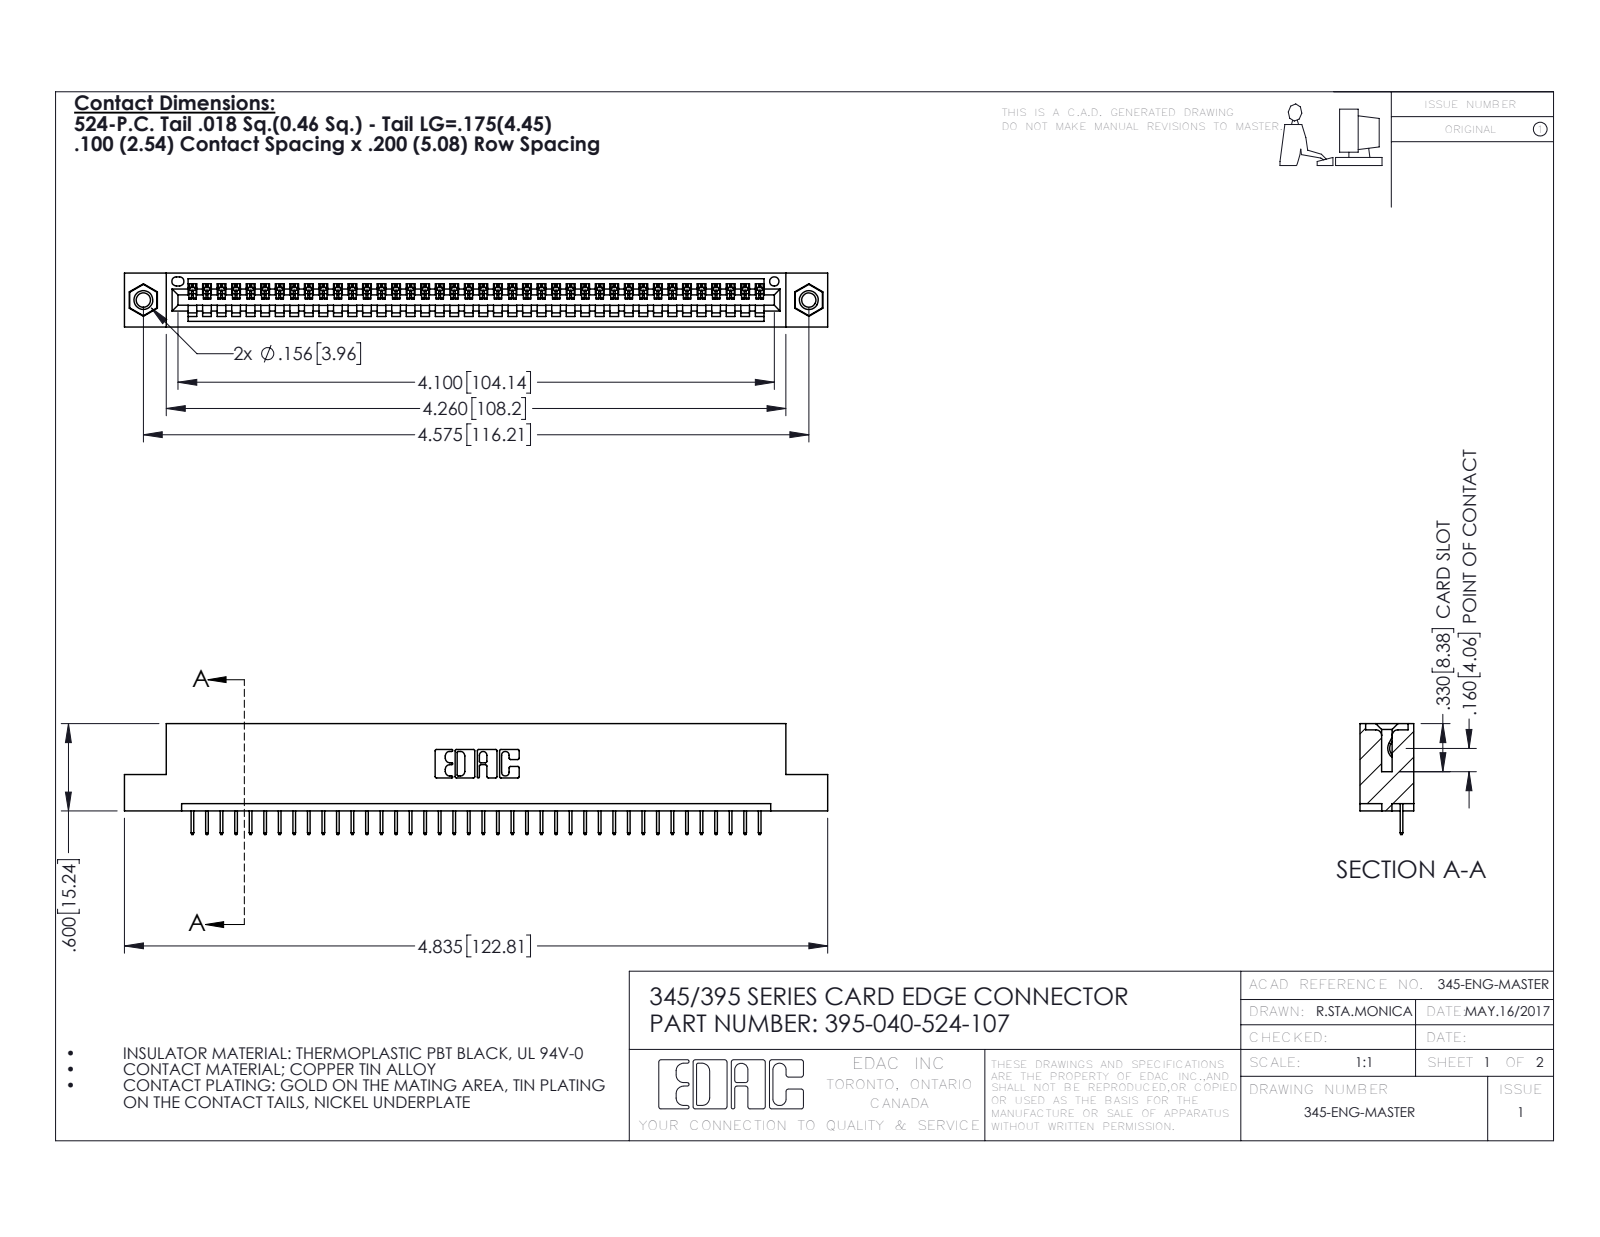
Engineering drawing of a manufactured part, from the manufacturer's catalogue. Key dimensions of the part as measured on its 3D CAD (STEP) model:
Part name (STEP PRODUCT): 395-040-524-107; 345-292-001_345-293-124; 345 Part_Flush Mounting Lugs - 0.156 Dia-TI; 345-250-001_345-250-005-103
STEP written by: SolidWorks 2016 (CONFIG_CONTROL_DESIGN)
Units: inches
Bodies: 43 solids, 2666 faces (1952 planar, 698 cylindrical, 16 other)
Overall size (bounding box): 4.835 × 0.762 × 0.37
Volume: 0.7 in³ · Surface area: 22.86 in²
Round holes (diameter × count): ⌀0.098 ×2, ⌀0.125 ×2, ⌀0.156 ×2, ⌀0.064 ×1
Round bosses / shafts (diameter × count): ⌀0.155 ×2
Partial cylindrical surfaces — rounded edges, fillets, slot ends (radius × count): R0.006 ×80, R0.01 ×22, R0.007 ×6, R0.031 ×6, R0.026 ×3, R0.031 ×2, R0.04 ×2, R0.014 ×1
Main face-to-face distances: 0.072, 0.298, 0.37, 0.2, 0.098, 0.272, 0.025, 0.225, 0.072, 0.149
Hole centre spacings: 0.27, 4.339, 4.575
